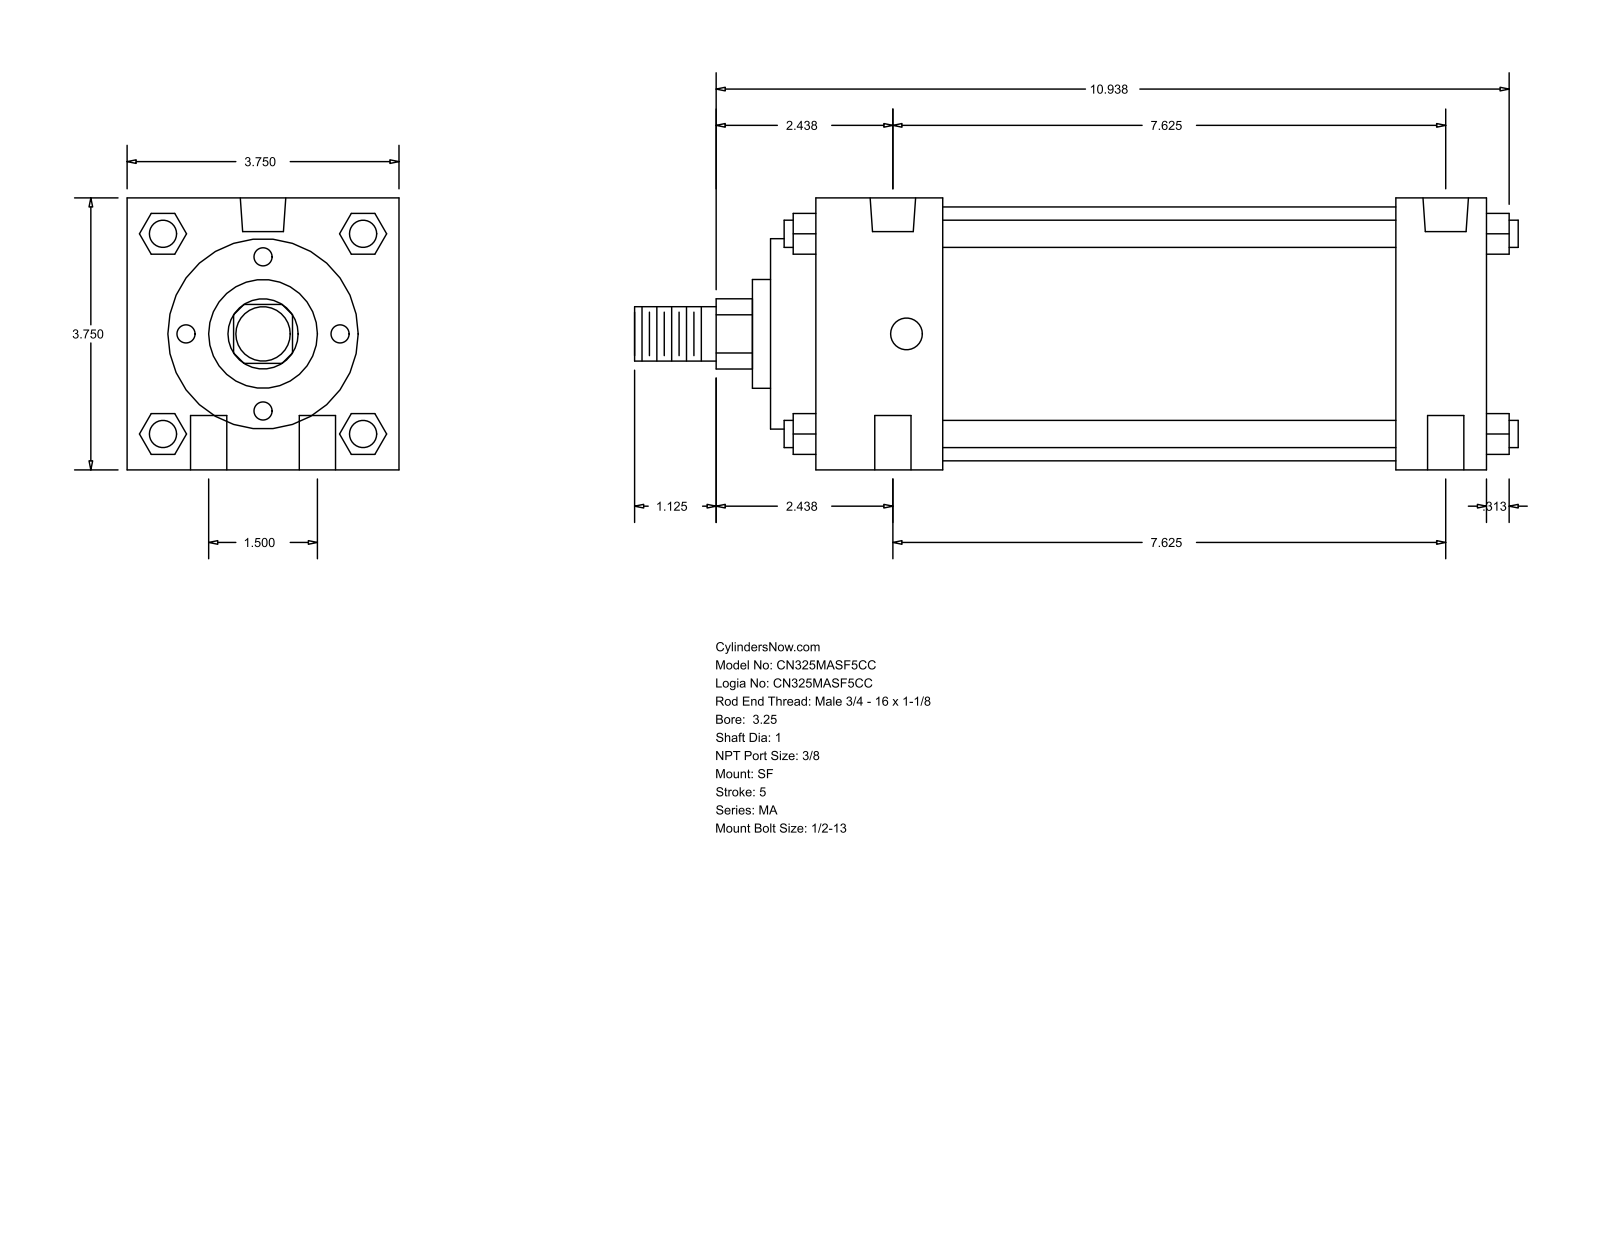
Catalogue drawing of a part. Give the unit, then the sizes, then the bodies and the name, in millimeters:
Units: millimetres
Overall size (bounding box): 309.56 × 95.25 × 95.25
Round holes (diameter × count): ⌀12.7 ×4, ⌀11.11 ×2, ⌀15.93 ×2
Round bosses / shafts (diameter × count): ⌀9.53 ×4, ⌀88.9 ×1, ⌀66.67 ×1, ⌀38.1 ×1, ⌀25.4 ×1, ⌀19.05 ×1
Partial cylindrical surfaces — rounded edges, fillets, slot ends (radius × count): R12.29 ×1
Main face-to-face distances: 95.24, 234.96, 203.2, 31.76, 44.46, 158.74, 190.5, 15.87, 60.33, 219.07
Hole centre spacings: 19.05, 194.61, 193.68, 38.1, 197.39, 184.15
Bodies: 0 solids, 126 faces (95 planar, 31 cylindrical, 0 other)
Part name (STEP PRODUCT): MA_SF__0325_1
STEP written by: GSSL Pune (CONFIG_CONTROL_DESIGN)
